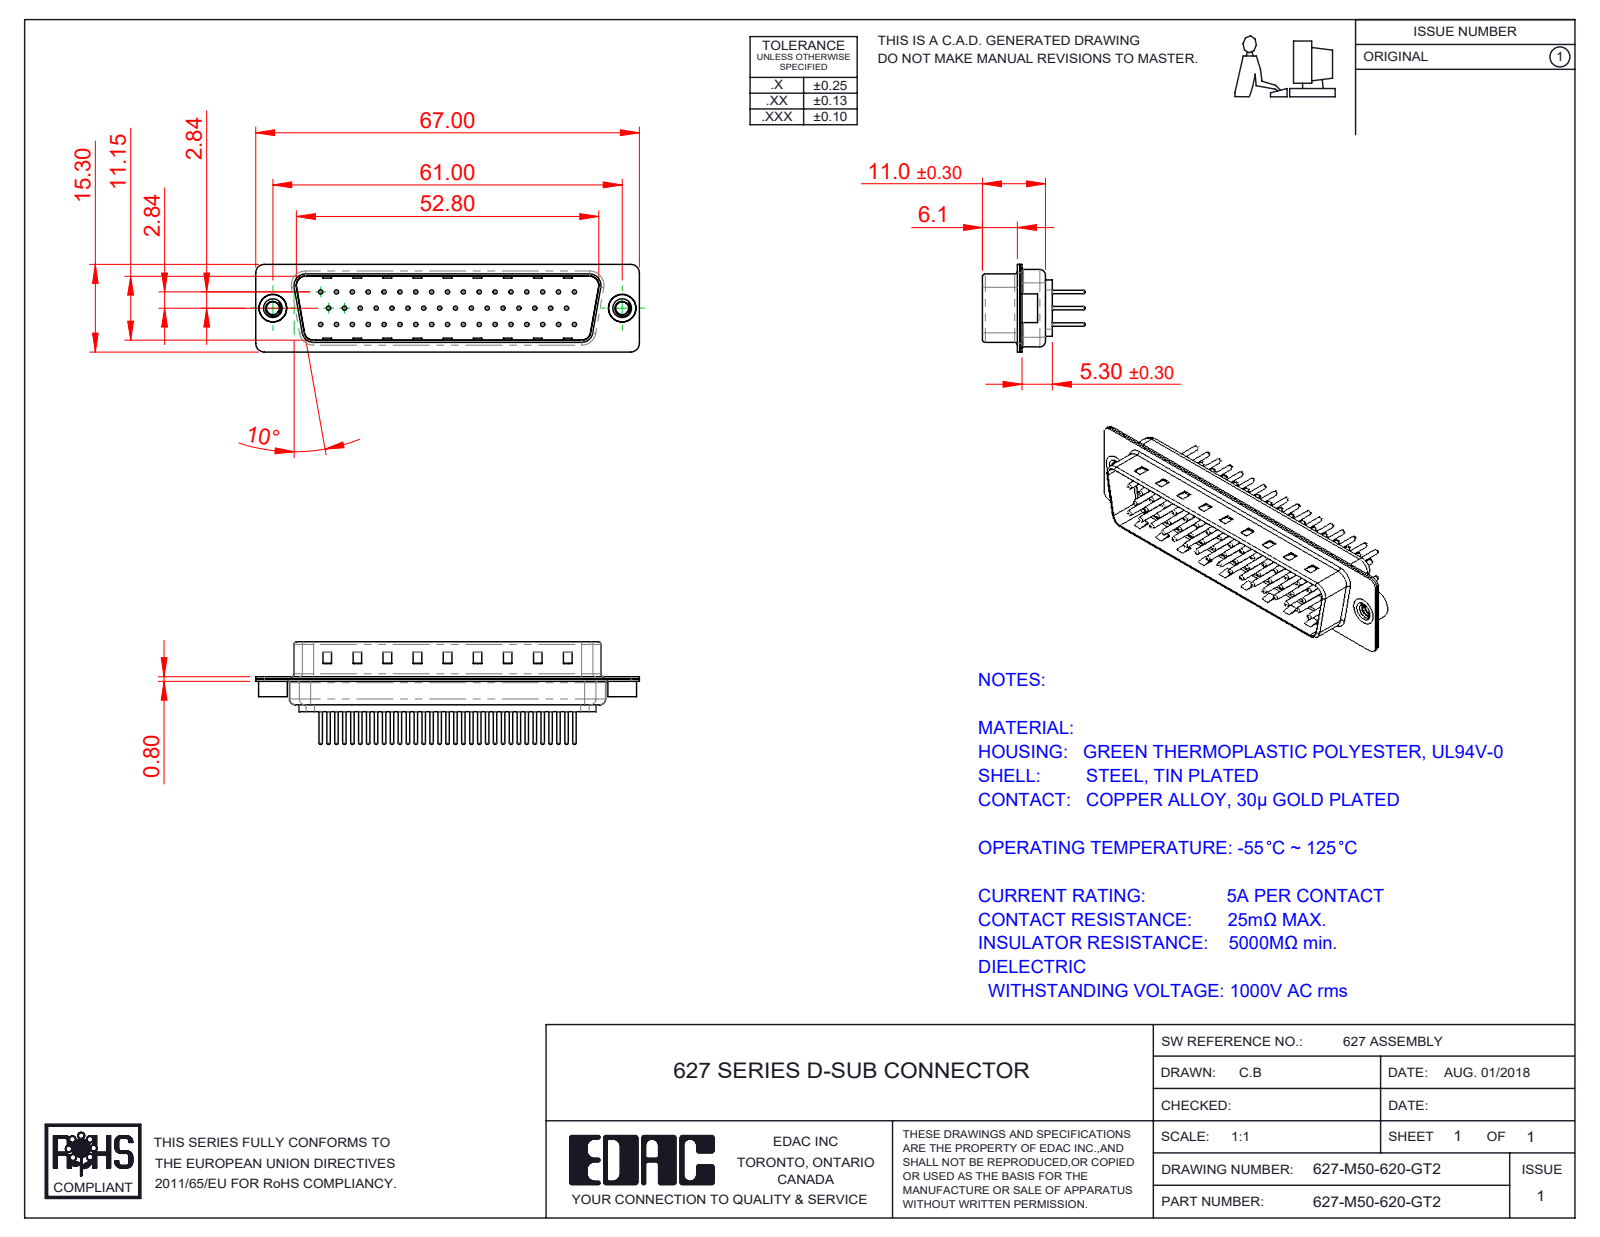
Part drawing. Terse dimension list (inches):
name: 627M Housing_50 Contacts; 627M Contact Row 2_20; 627M Contact Row 3_20; 627M Shell Front_50 Contacts (+4 more)
written by: SolidWorks 2020 (CONFIG_CONTROL_DESIGN)
unit: in
bodies: 55 solids, 2262 faces (553 planar, 841 cylindrical, 868 other)
size: 2.638 × 0.705 × 0.602
volume: 0.276 in³; area: 16.58 in²
holes: 50× ⌀0.03, 50× ⌀0.063, 50× ⌀0.079, 2× ⌀0.089, 2× ⌀0.157, 2× ⌀0.189
bosses: 50× ⌀0.059, 50× ⌀0.024, 2× ⌀0.197, 2× ⌀0.193
rounds: 16× R0.059, 12× R0.079, 8× R0.02, 8× R0.063, 4× R0.01, 4× R0.024, 4× R0.026, 4× R0.035
face distances: 0.016, 0.455, 0.224, 0.24, 0.031, 0.03, 0.485, 0.485, 0.516, 0.209
hole spacings: 0.124, 0.109, 0.218, 0.327, 0.436, 0.545, 0.654, 0.198
